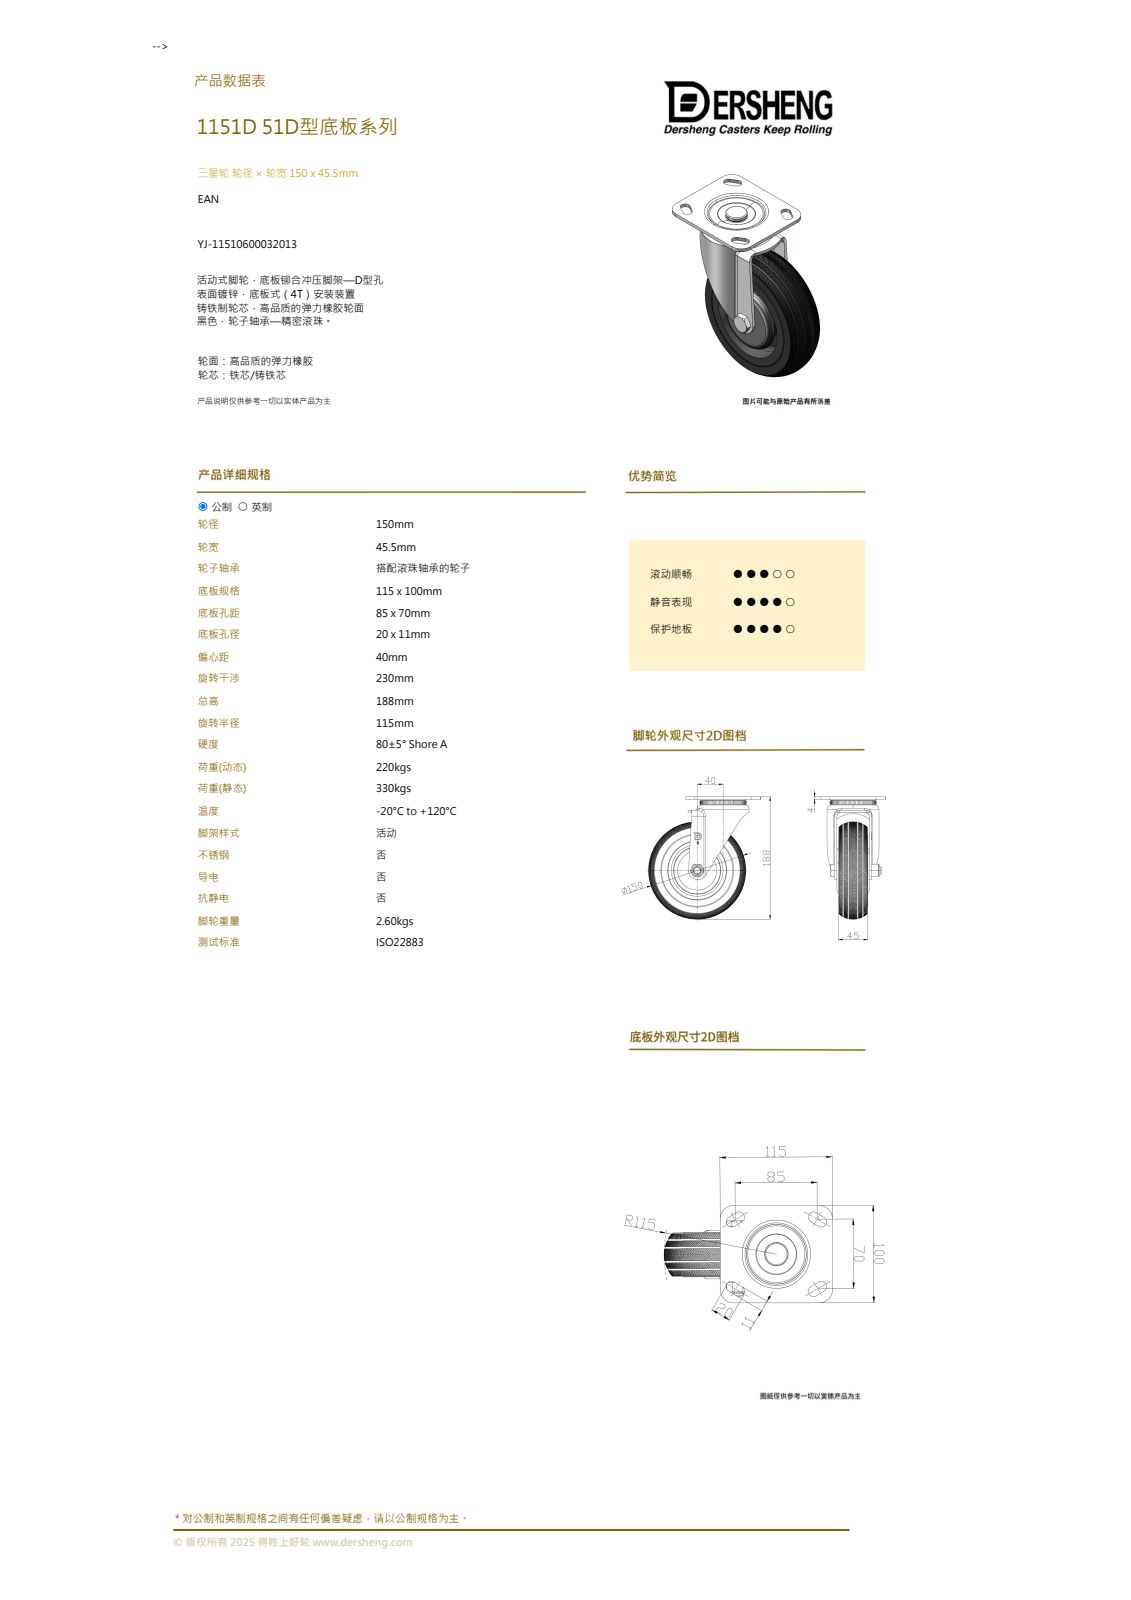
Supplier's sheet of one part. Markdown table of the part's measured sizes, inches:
| quantity | value |
| --- | --- |
| part name | 葩璃 (3) ^_11510600452013.STEP; ^11510600452013.STEP; ^_11510600452013.STEP; 葩璃 (4) ^_11510600452013.STEP (+3 more) |
| STEP written by | SolidWorks 2021 (CONFIG_CONTROL_DESIGN) |
| units | inches |
| bodies | 10 solids, 4735 faces (2565 planar, 182 cylindrical, 1988 other) |
| overall size | 7.412 × 6.799 × 3.956 |
| volume | 41.05 in³ |
| surface area | 302.8 in² |
| round holes (diameter × count) | 0.472 × 1, 0.492 × 1, 0.497 × 1, 0.945 × 1, 2.495 × 1, 4.331 × 1 |
| round bosses / shafts (diameter × count) | 5.197 × 1, 1.165 × 1, 0.931 × 1, 0.748 × 1, 0.63 × 1 |
| partial cylindrical surfaces (radius × count) | 0.215 × 8, 0.551 × 4, 0.039 × 2, 0.236 × 2, 0.374 × 2, 0.472 × 2, 0.17 × 1, 0.217 × 1 |
| main face-to-face distances | 0.089, 1.88, 1.053, 0.098, 1.87, 1.781, 0.138, 0.157, 0.236, 0.043 |
